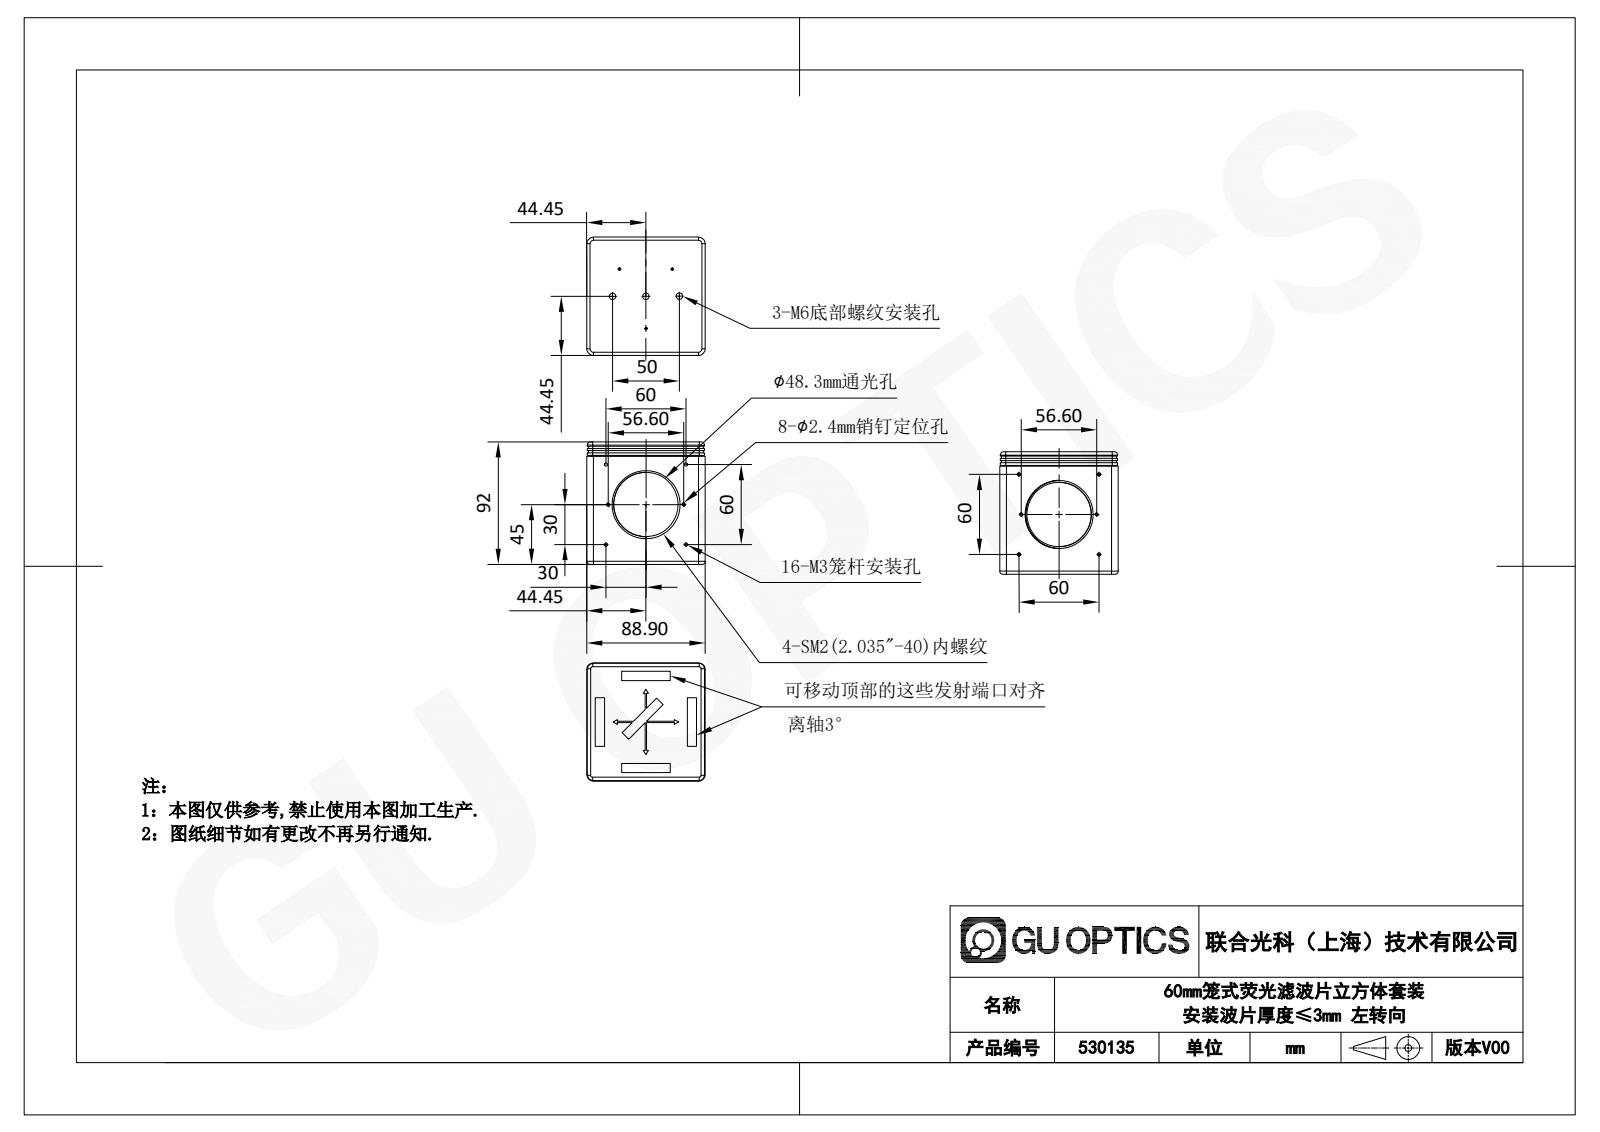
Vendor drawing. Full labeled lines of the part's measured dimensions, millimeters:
Part name (STEP PRODUCT): 530135
STEP written by: SolidWorks 2020 (CONFIG_CONTROL_DESIGN)
Units: millimetres
Bodies: 0 solids, 200 faces (100 planar, 84 cylindrical, 16 other)
Overall size (bounding box): 92 × 88.9 × 88.9
Round bosses / shafts (diameter × count): ⌀2.5 ×8, ⌀2.4 ×4, ⌀5 ×3, ⌀2 ×3, ⌀52.17 ×2, ⌀52.1 ×2, ⌀51.17 ×2, ⌀51.1 ×2
Partial cylindrical surfaces — rounded edges, fillets, slot ends (radius × count): R2.5 ×8, R3.2 ×4, R4 ×4, R5 ×4, R1.8 ×2, R7.6 ×2, R0.74 ×1
Main face-to-face distances: 5.1, 83.8, 88.9, 92, 0.6, 78.7, 83.2, 78.1, 5.7, 5.73
